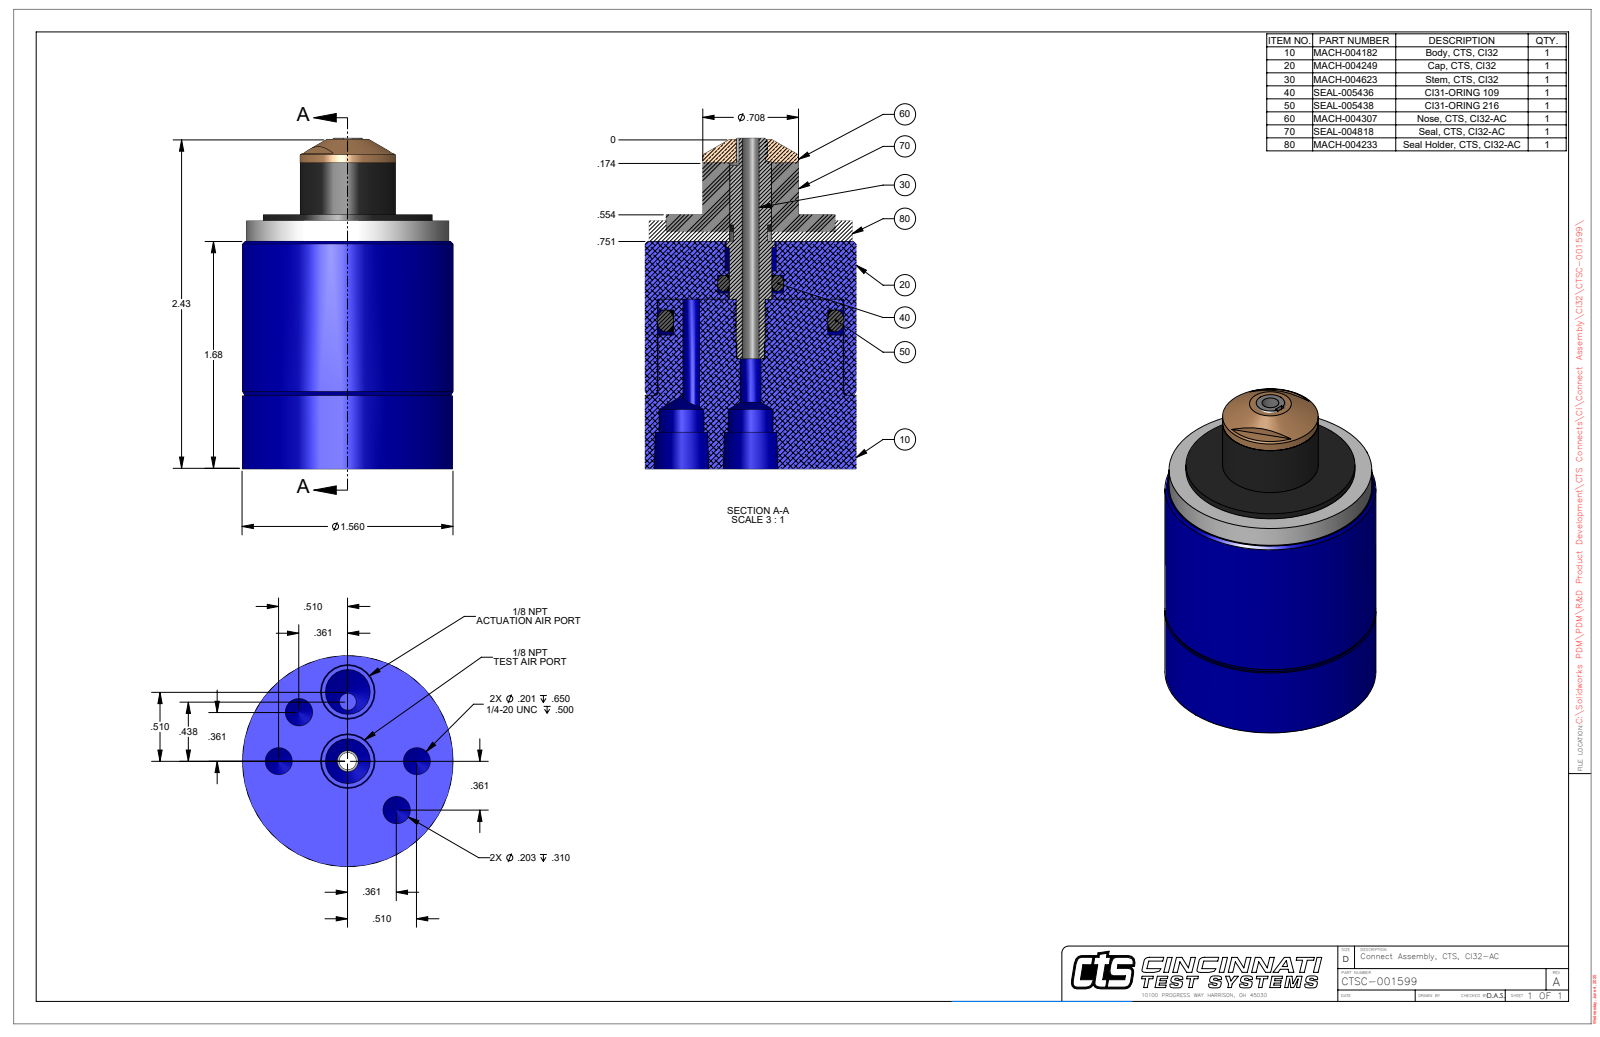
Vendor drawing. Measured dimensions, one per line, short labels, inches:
name: CTSC-001599
written by: SolidWorks 2023 (AUTOMOTIVE_DESIGN)
unit: in
bodies: 1 solid, 103 faces (30 planar, 41 cylindrical, 32 other)
size: 2.437 × 1.56 × 1.56
volume: 3.52 in³; area: 19.85 in²
holes: 2× ⌀0.125, 2× ⌀0.201, 2× ⌀0.203, 2× ⌀0.332, 1× ⌀0.156, 1× ⌀0.314, 1× ⌀0.38, 1× ⌀1.377
bosses: 1× ⌀1.56, 1× ⌀1.5, 1× ⌀1.365, 1× ⌀1.25, 1× ⌀0.708, 1× ⌀0.357, 1× ⌀0.31
rounds: 1× R0.106
face distances: 1.874, 1.829, 0.045, 0.542, 1.287, 1.332, 0.273, 0.269, 1.556, 1.601
hole spacings: 0.51, 0.39, 0.942, 0.672, 0.721, 0.072, 0.369, 0.437
